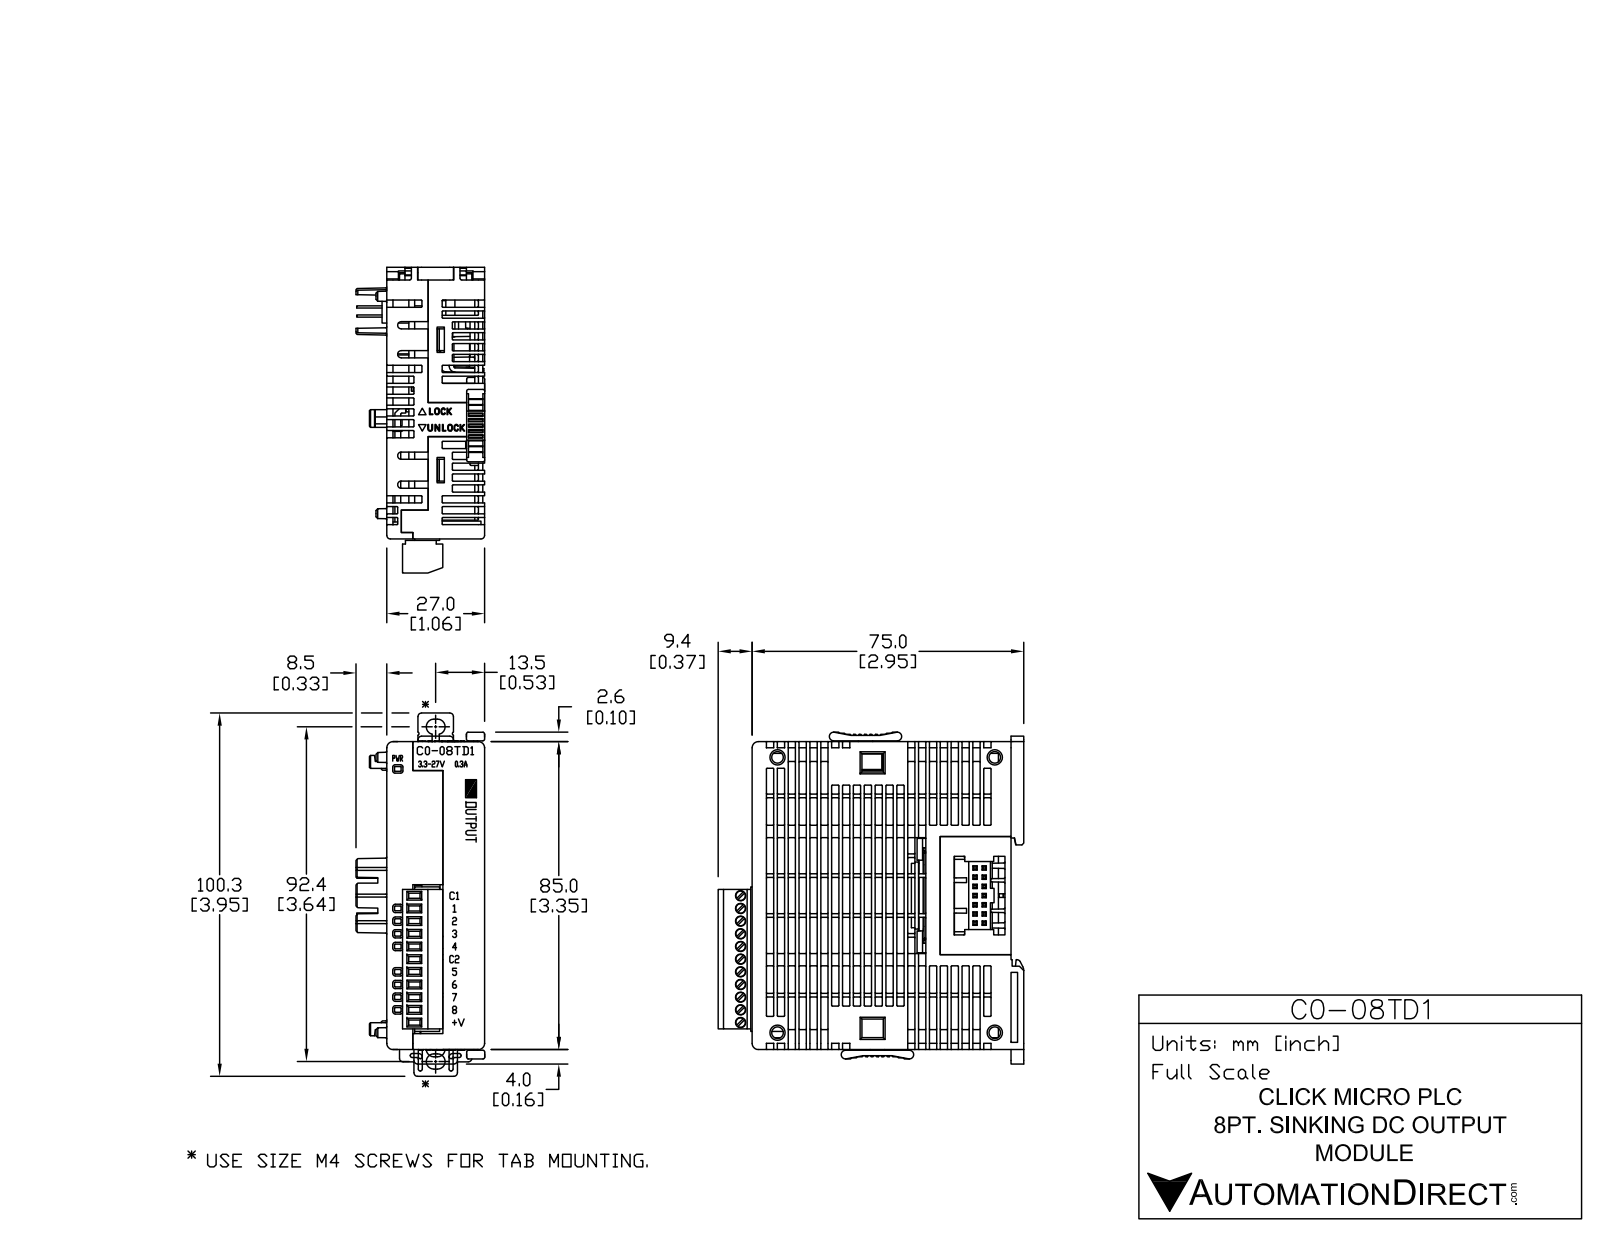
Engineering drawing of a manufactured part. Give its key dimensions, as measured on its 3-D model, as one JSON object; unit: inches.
{"part_name": "C0-08TD1", "step_written_by": "SolidWorks 2009 (AUTOMOTIVE_DESIGN)", "units": "inches", "bodies": {"solids": 1, "faces": 3689, "planar": 2637, "cylindrical": 968, "other": 84}, "overall_size": [3.606, 3.323, 1.4], "volume_in3": 9.917, "surface_area_in2": 49.24, "round_holes": [[0.039, 11], [0.11, 11], [0.126, 4], [0.079, 2]], "round_bosses_or_shafts": [[0.102, 11], [0.075, 1]], "partial_cylinders_radius": [[0.008, 570], [0.02, 43], [0.012, 22], [0.039, 18], [0.047, 12], [0.11, 11], [0.067, 6], [0.083, 4]], "face_to_face_distances": [1.063, 0.02, 0.02, 1.043, 2.815, 0.067, 3.346, 1.035, 1.056, 3.327], "hole_center_spacings": [0.138, 0.276, 0.413, 0.551, 0.689, 0.827, 0.965, 1.102]}
